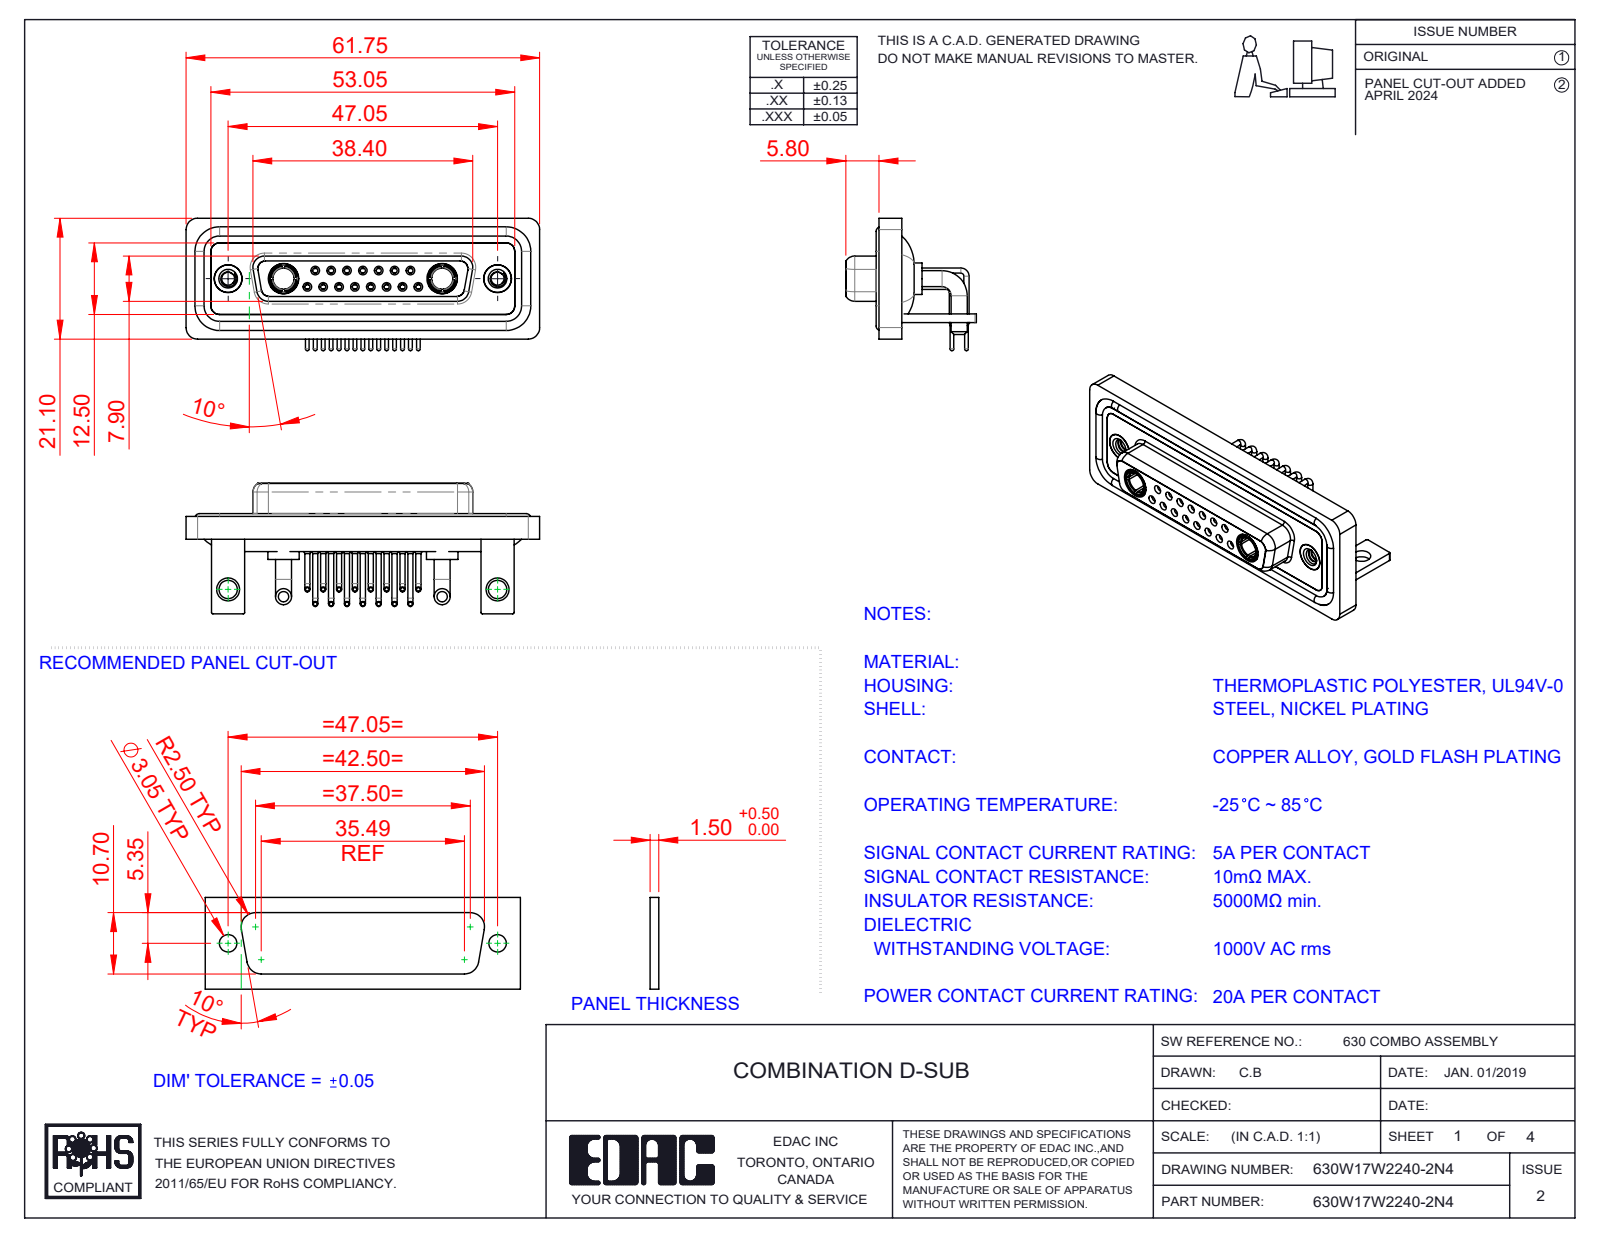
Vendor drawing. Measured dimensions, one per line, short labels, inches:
name: 630Combo Contact Row 1_50 Contacts; 630Combo Stabilizer Bracket_50 Contacts; 630Combo Threaded Rivet_2; 630Combo Housing_17W2 (+6 more)
written by: SolidWorks 2023 (CONFIG_CONTROL_DESIGN)
unit: in
bodies: 28 solids, 1385 faces (408 planar, 607 cylindrical, 370 other)
size: 2.431 × 0.91 × 0.898
volume: 0.54 in³; area: 23.66 in²
holes: 15× ⌀0.035, 15× ⌀0.043, 15× ⌀0.059, 15× ⌀0.079, 8× ⌀0.063, 7× ⌀0.067, 4× ⌀0.191, 2× ⌀0.089, 2× ⌀0.126, 2× ⌀0.146, 2× ⌀0.157, 2× ⌀0.159
bosses: 15× ⌀0.035, 15× ⌀0.026, 11× ⌀0.063, 4× ⌀0.11, 2× ⌀0.217, 2× ⌀0.205, 2× ⌀0.195, 2× ⌀0.195
rounds: 19× R0.079, 18× R0.059, 16× R0.01, 8× R0.053, 8× R0.063, 5× R0.02, 4× R0.024, 4× R0.026
face distances: 0.016, 0.071, 0.114, 0.146, 0.059, 0.161, 0.043, 0.055, 0.063, 0.122
hole spacings: 0.124, 0.109, 0.218, 0.327, 0.198, 0.295, 0.436, 0.198
